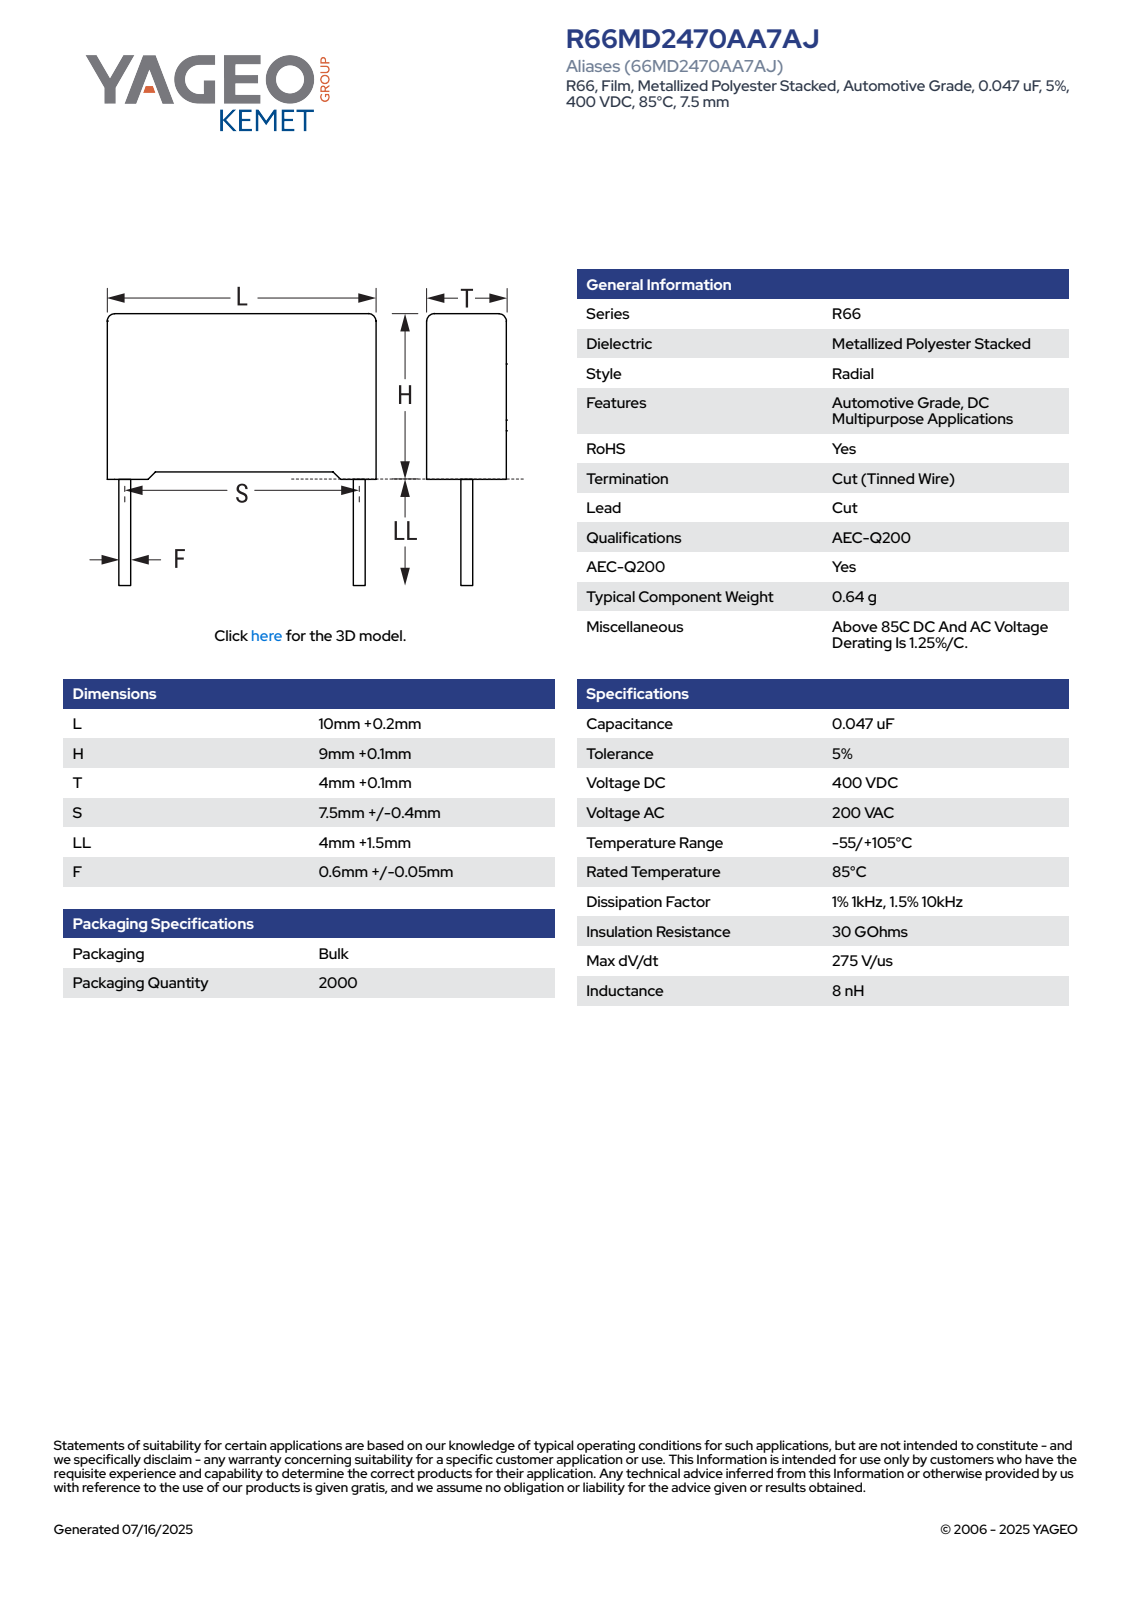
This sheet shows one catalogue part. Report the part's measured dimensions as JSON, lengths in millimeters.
{"part_name": "CFR_RB2_10X9X4_L10.2H9.1T4.1S7.5LL5.5F0.65", "step_written_by": "SolidWorks 2021 (AUTOMOTIVE_DESIGN)", "units": "millimeters", "bodies": {"solids": 4, "faces": 85, "planar": 77, "cylindrical": 8, "other": 0}, "overall_size": [14.6, 10.2, 4.11], "volume_mm3": 358, "surface_area_mm2": 385, "round_bosses_or_shafts": [[0.65, 2]], "partial_cylinders_radius": [[0.5, 4]], "face_to_face_distances": [4.1, 10.2, 8.35, 0.34, 3.76, 0.75, 9.1, 3.42, 9.86, 0.31]}
